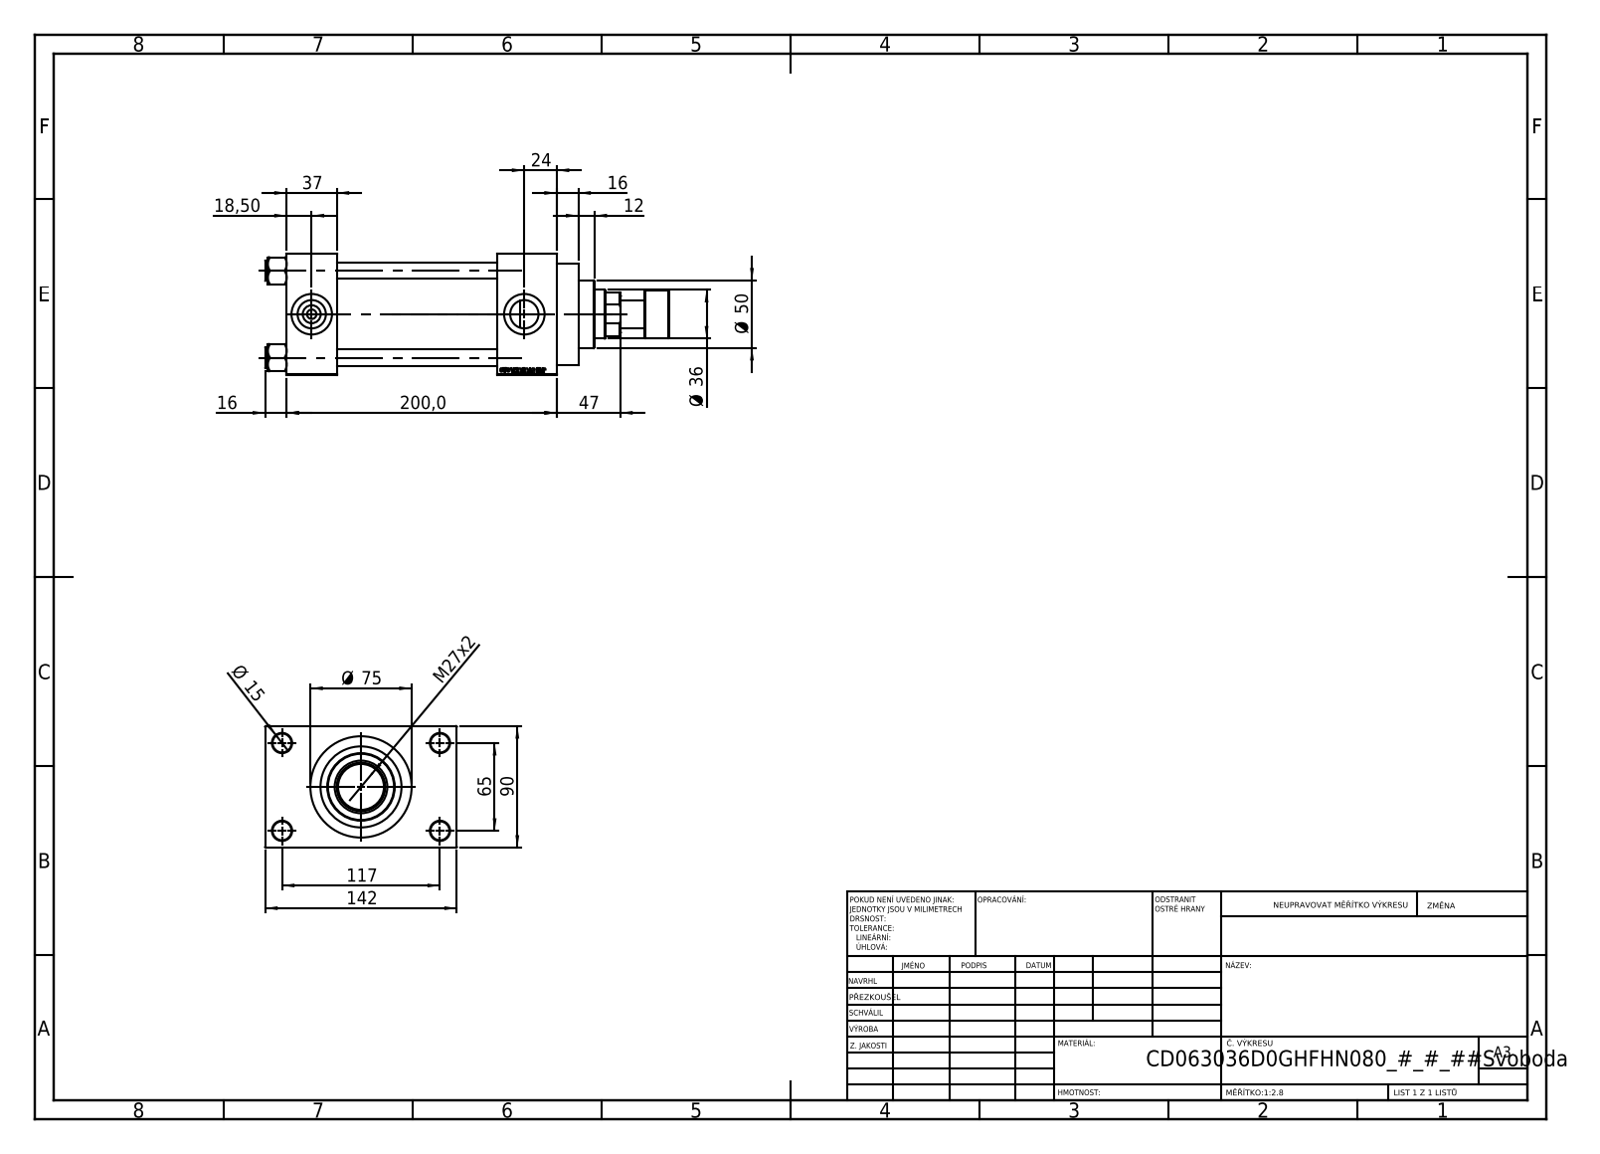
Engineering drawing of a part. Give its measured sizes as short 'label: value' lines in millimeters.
name: V215CD_NUT_M5_D; V215CD_D_Body; V215CD_D_TYCINKA; V215CR_ROD_END_F (+2 more)
written by: SolidWorks 2019 (CONFIG_CONTROL_DESIGN)
unit: mm
bodies: 12 solids, 1117 faces (501 planar, 92 cylindrical, 524 other)
size: 299 × 142 × 90
volume: 1 261 000 mm³; area: 252 066 mm²
holes: 4× ⌀12, 4× ⌀14, 2× ⌀7, 2× ⌀20.96, 2× ⌀30, 1× ⌀25.5, 1× ⌀36, 1× ⌀39, 1× ⌀50, 1× ⌀60, 1× ⌀63
bosses: 4× ⌀15, 1× ⌀75, 1× ⌀69, 1× ⌀35, 1× ⌀21
face distances: 90, 119, 37, 156, 200, 163, 44, 26, 116, 142
hole spacings: 26.35, 45.47, 64.3, 66.92, 69.81, 90.65, 111.34, 65
